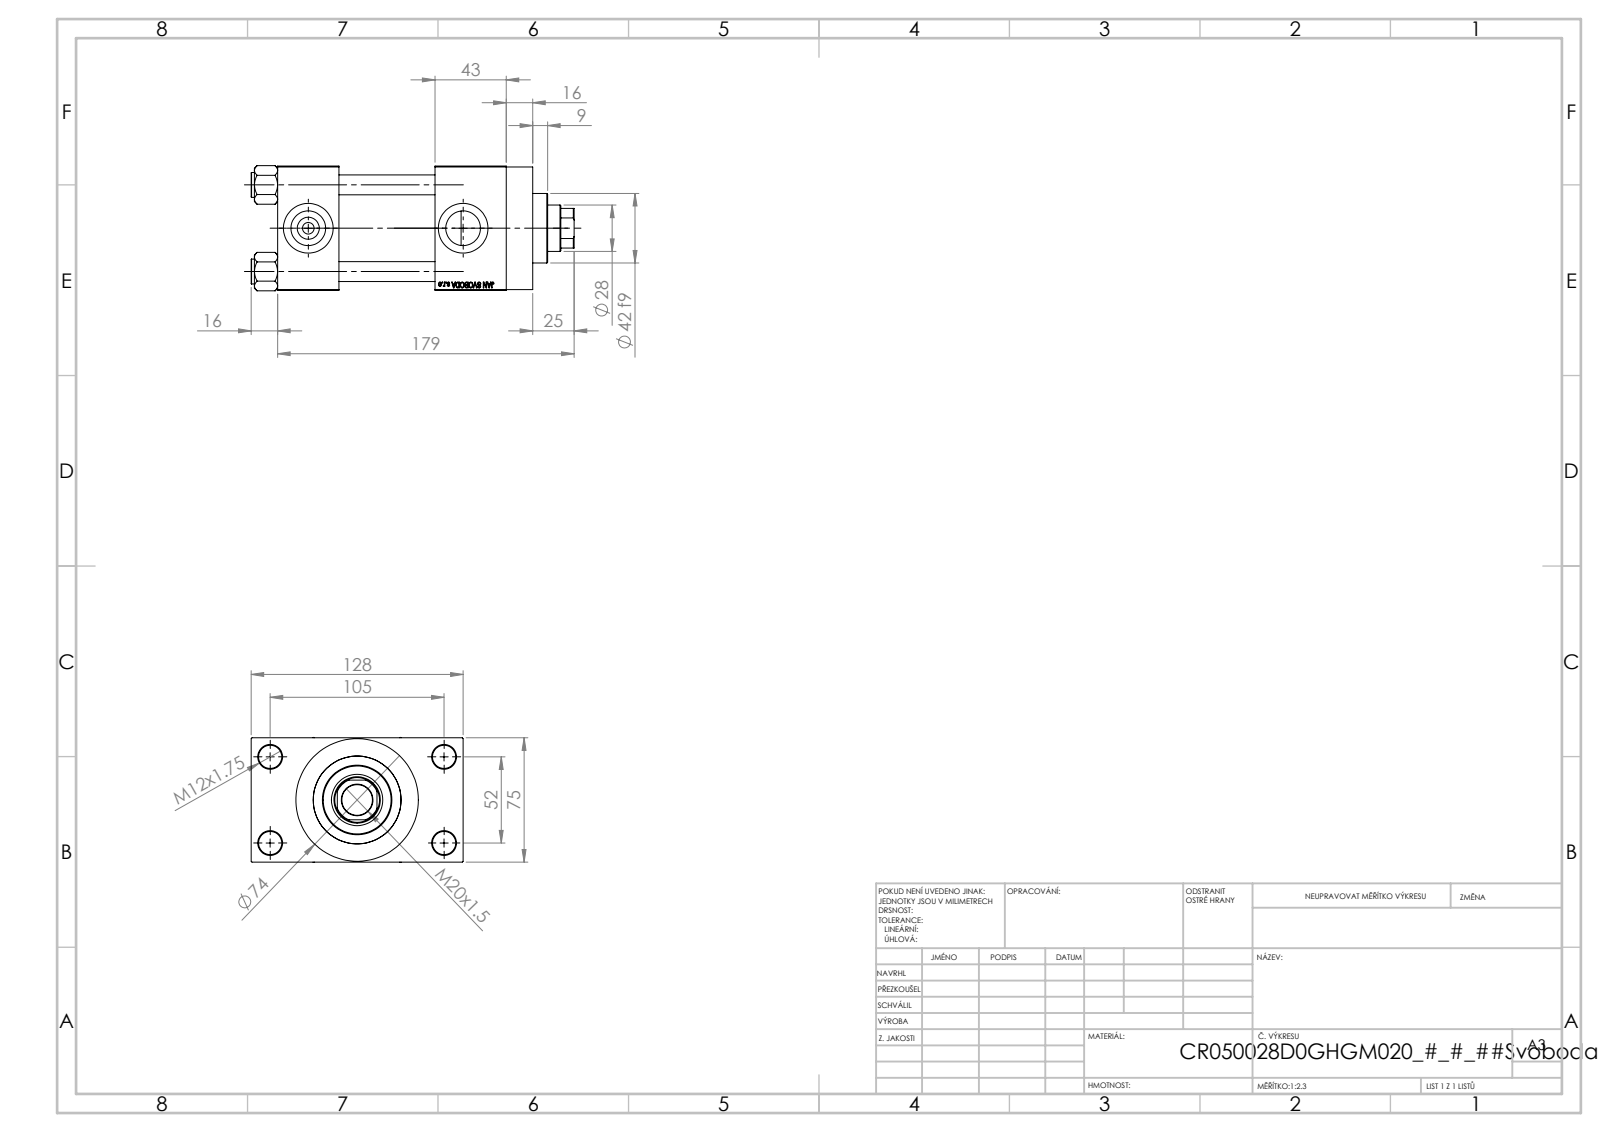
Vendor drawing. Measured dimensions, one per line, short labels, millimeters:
name: NUT_M5_D; V215CR_VCP_D; V215_VC_A; V215CR_D_TYCINKA (+1 more)
written by: SolidWorks 2019 (CONFIG_CONTROL_DESIGN)
unit: mm
bodies: 11 solids, 1103 faces (497 planar, 88 cylindrical, 518 other)
size: 195 × 128 × 75.54
volume: 806 210 mm³; area: 170 608 mm²
holes: 4× ⌀12, 4× ⌀14, 2× ⌀7, 2× ⌀20.96, 2× ⌀30, 1× ⌀18.5, 1× ⌀28, 1× ⌀31, 1× ⌀41, 1× ⌀50, 1× ⌀53
bosses: 4× ⌀15, 1× ⌀74, 1× ⌀56, 1× ⌀42
rounds: 1× R13.5
face distances: 75, 58, 37, 95, 26.5, 138, 101, 43, 101.5, 16
hole spacings: 26.35, 36.98, 52.3, 58.43, 58.59, 78.65, 94.37, 52
